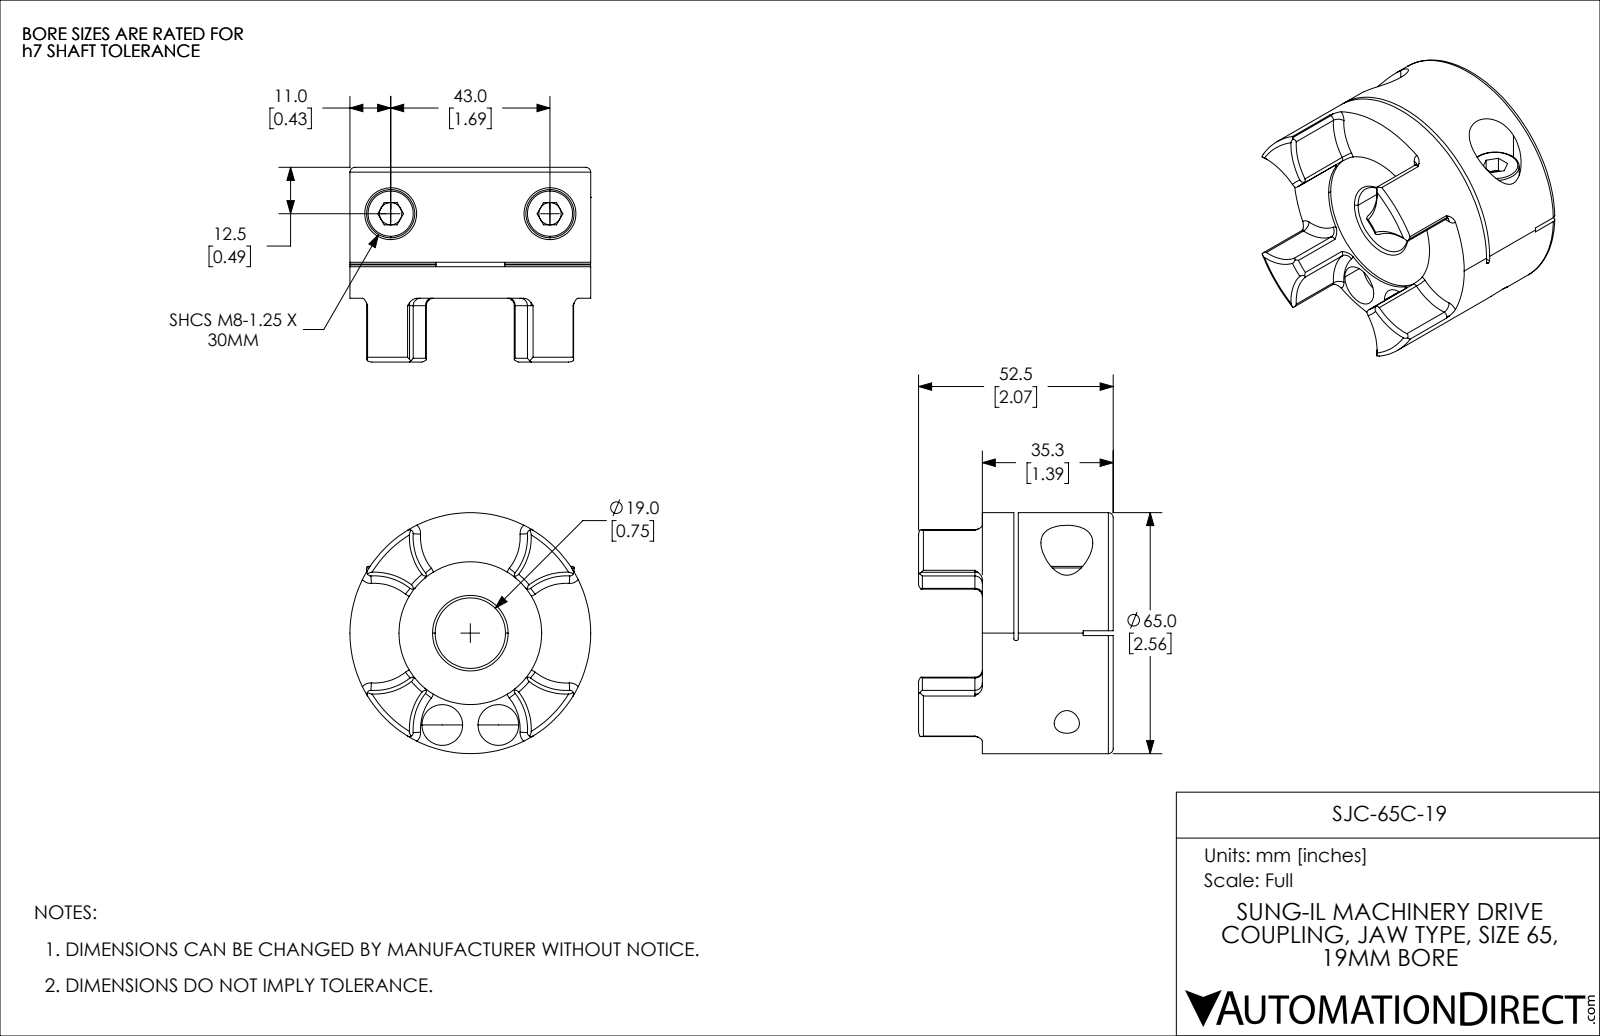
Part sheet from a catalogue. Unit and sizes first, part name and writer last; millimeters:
Units: millimetres
Overall size (bounding box): 65 × 65 × 52.5
Round holes (diameter × count): ⌀6 ×2, ⌀6.8 ×2, ⌀8.5 ×2, ⌀11 ×2, ⌀14 ×2, ⌀19 ×1, ⌀38.5 ×1
Round bosses / shafts (diameter × count): ⌀13 ×2, ⌀8 ×2, ⌀65 ×1
Partial cylindrical surfaces — rounded edges, fillets, slot ends (radius × count): R1 ×16, R15.45 ×4, R0.5 ×2, R50 ×1
Main face-to-face distances: 26.8, 1.2, 25.6, 8.5, 9.7, 35.3, 1.3, 0.8, 7.7, 8.9
Hole centre spacings: 25.89, 15.14, 43
Volume: 108 608 mm³ · Surface area: 28 892 mm²
Bodies: 3 solids, 207 faces (52 planar, 73 cylindrical, 82 other)
Part name (STEP PRODUCT): SJC-65C-19
STEP written by: SolidWorks 2021 (CONFIG_CONTROL_DESIGN)
